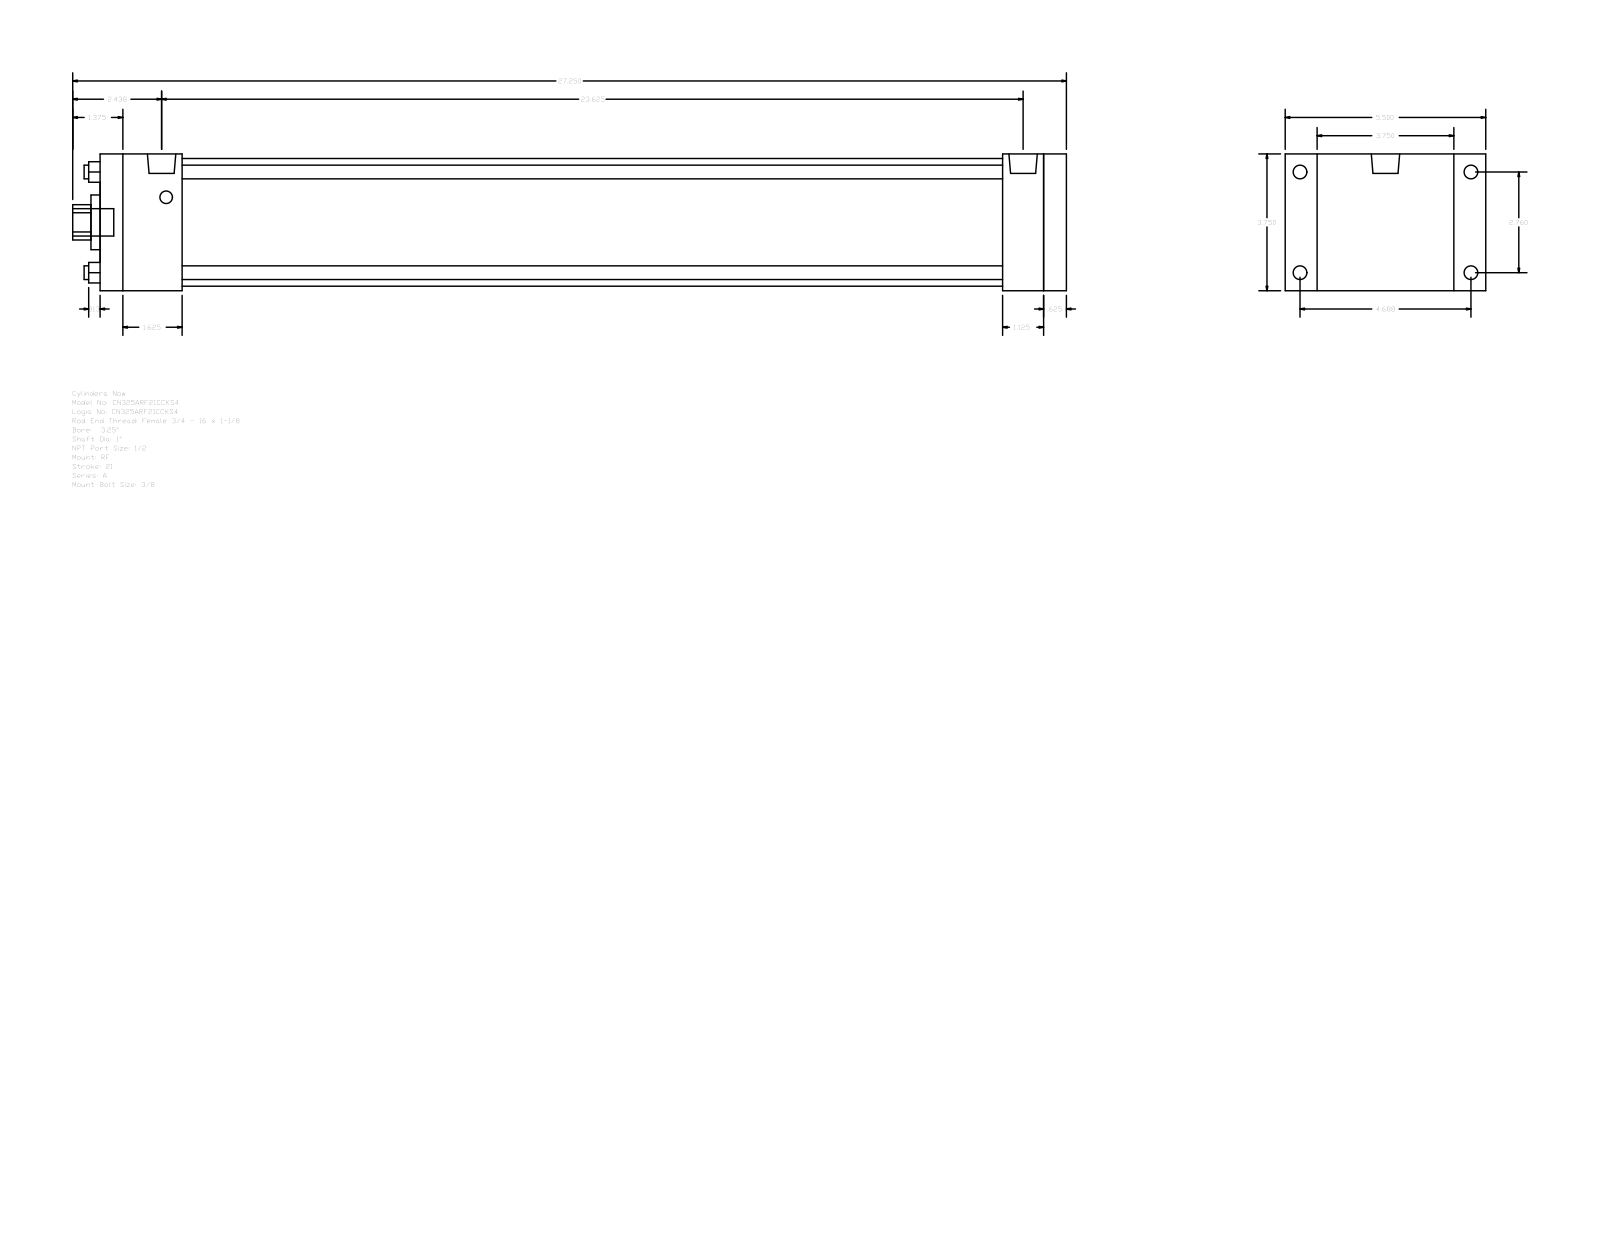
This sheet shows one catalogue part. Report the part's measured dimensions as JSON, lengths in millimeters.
{"part_name": "A_RF__0325_1", "step_written_by": "GSSL Pune (CONFIG_CONTROL_DESIGN)", "units": "millimeters", "bodies": {"solids": 0, "faces": 92, "planar": 64, "cylindrical": 28, "other": 0}, "overall_size": [692.15, 139.7, 95.25], "round_holes": [[9.53, 4], [25.4, 1], [38.1, 1], [88.9, 1]], "round_bosses_or_shafts": [[9.53, 4], [8.73, 4], [19.77, 2], [19.05, 1]], "partial_cylinders_radius": [[12.29, 1]], "face_to_face_distances": [95.24, 673.1, 657.22, 15.88, 22.23, 117.47, 28.57, 628.65, 44.45, 57.15], "hole_center_spacings": [49.57, 70.1, 99.14]}
